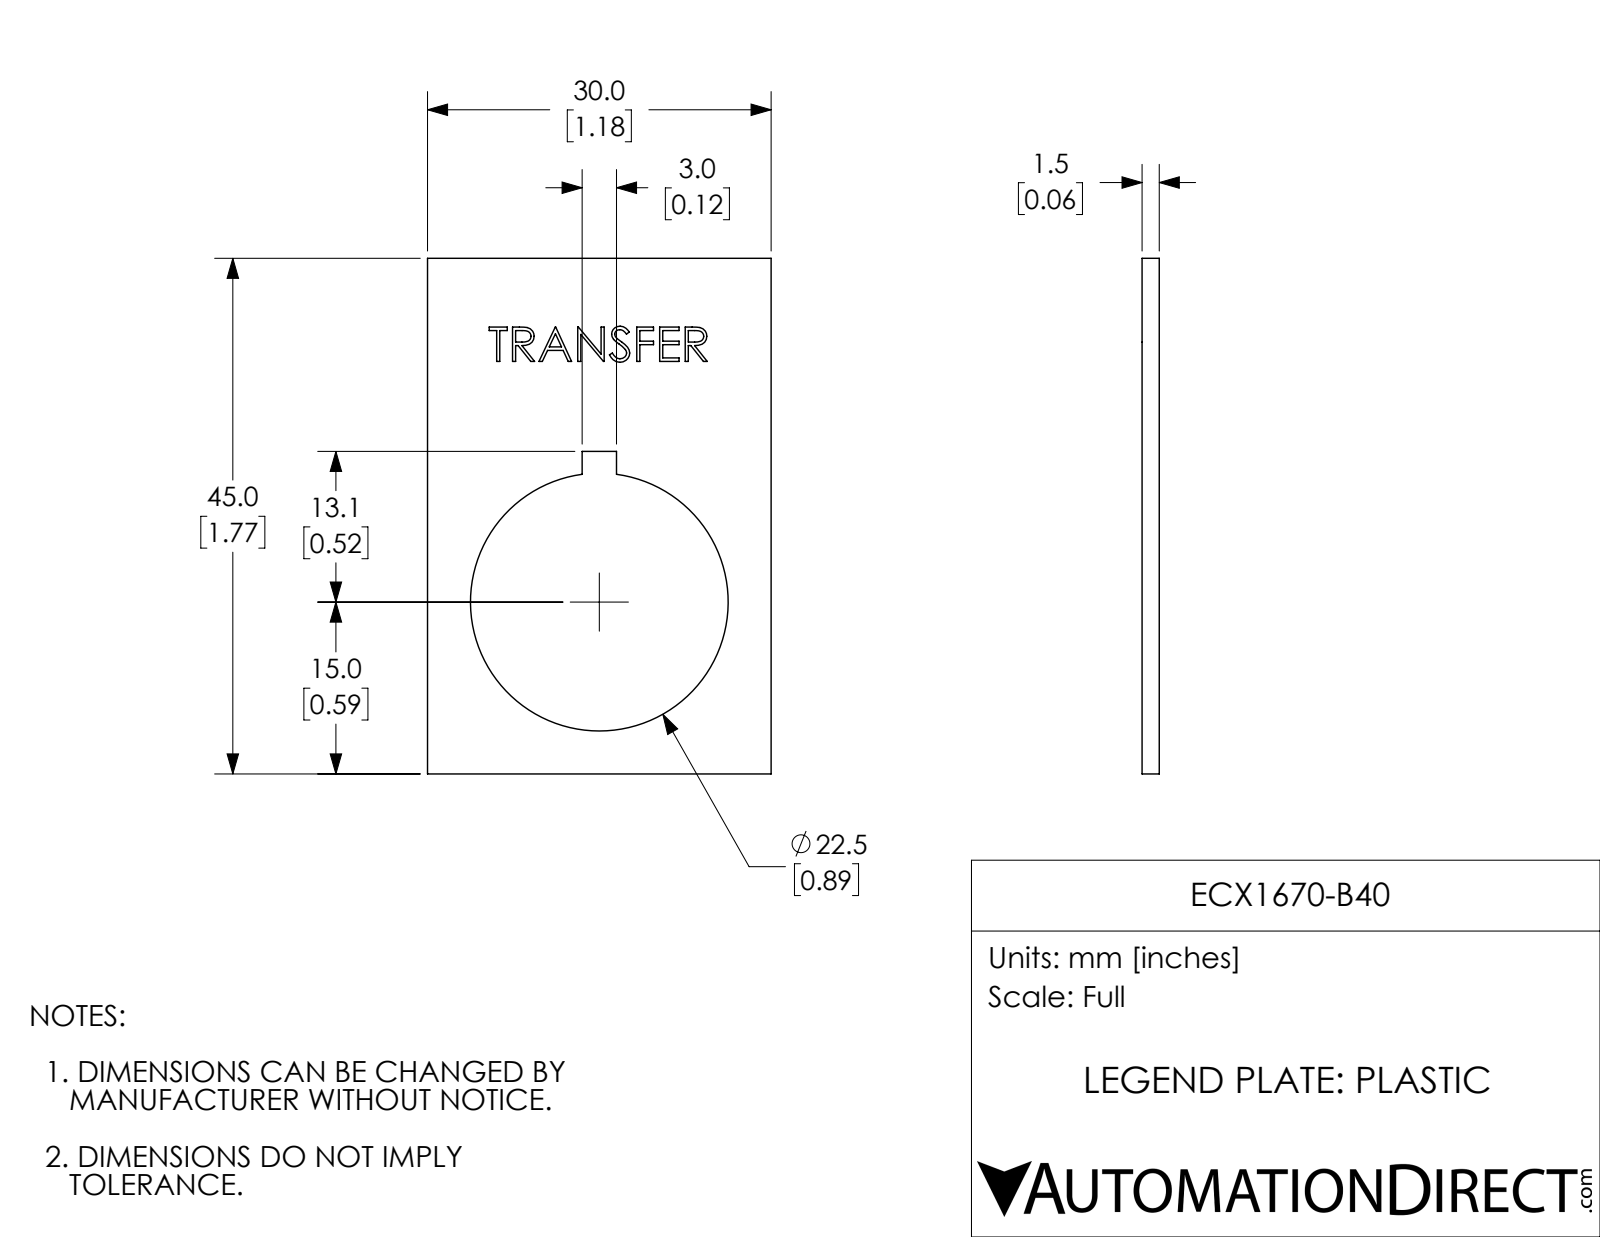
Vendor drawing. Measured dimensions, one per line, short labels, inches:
name: ECX1670-B40
written by: SolidWorks 2017 (AUTOMOTIVE_DESIGN)
unit: in
bodies: 1 solid, 123 faces (95 planar, 3 cylindrical, 25 other)
size: 1.772 × 1.181 × 0.059
volume: 0.087 in³; area: 3.461 in²
holes: 1× ⌀0.886
face distances: 0.059, 1.181, 1.772, 0.058, 0.531, 0.65, 1.108, 0.663, 0.118, 0.427
